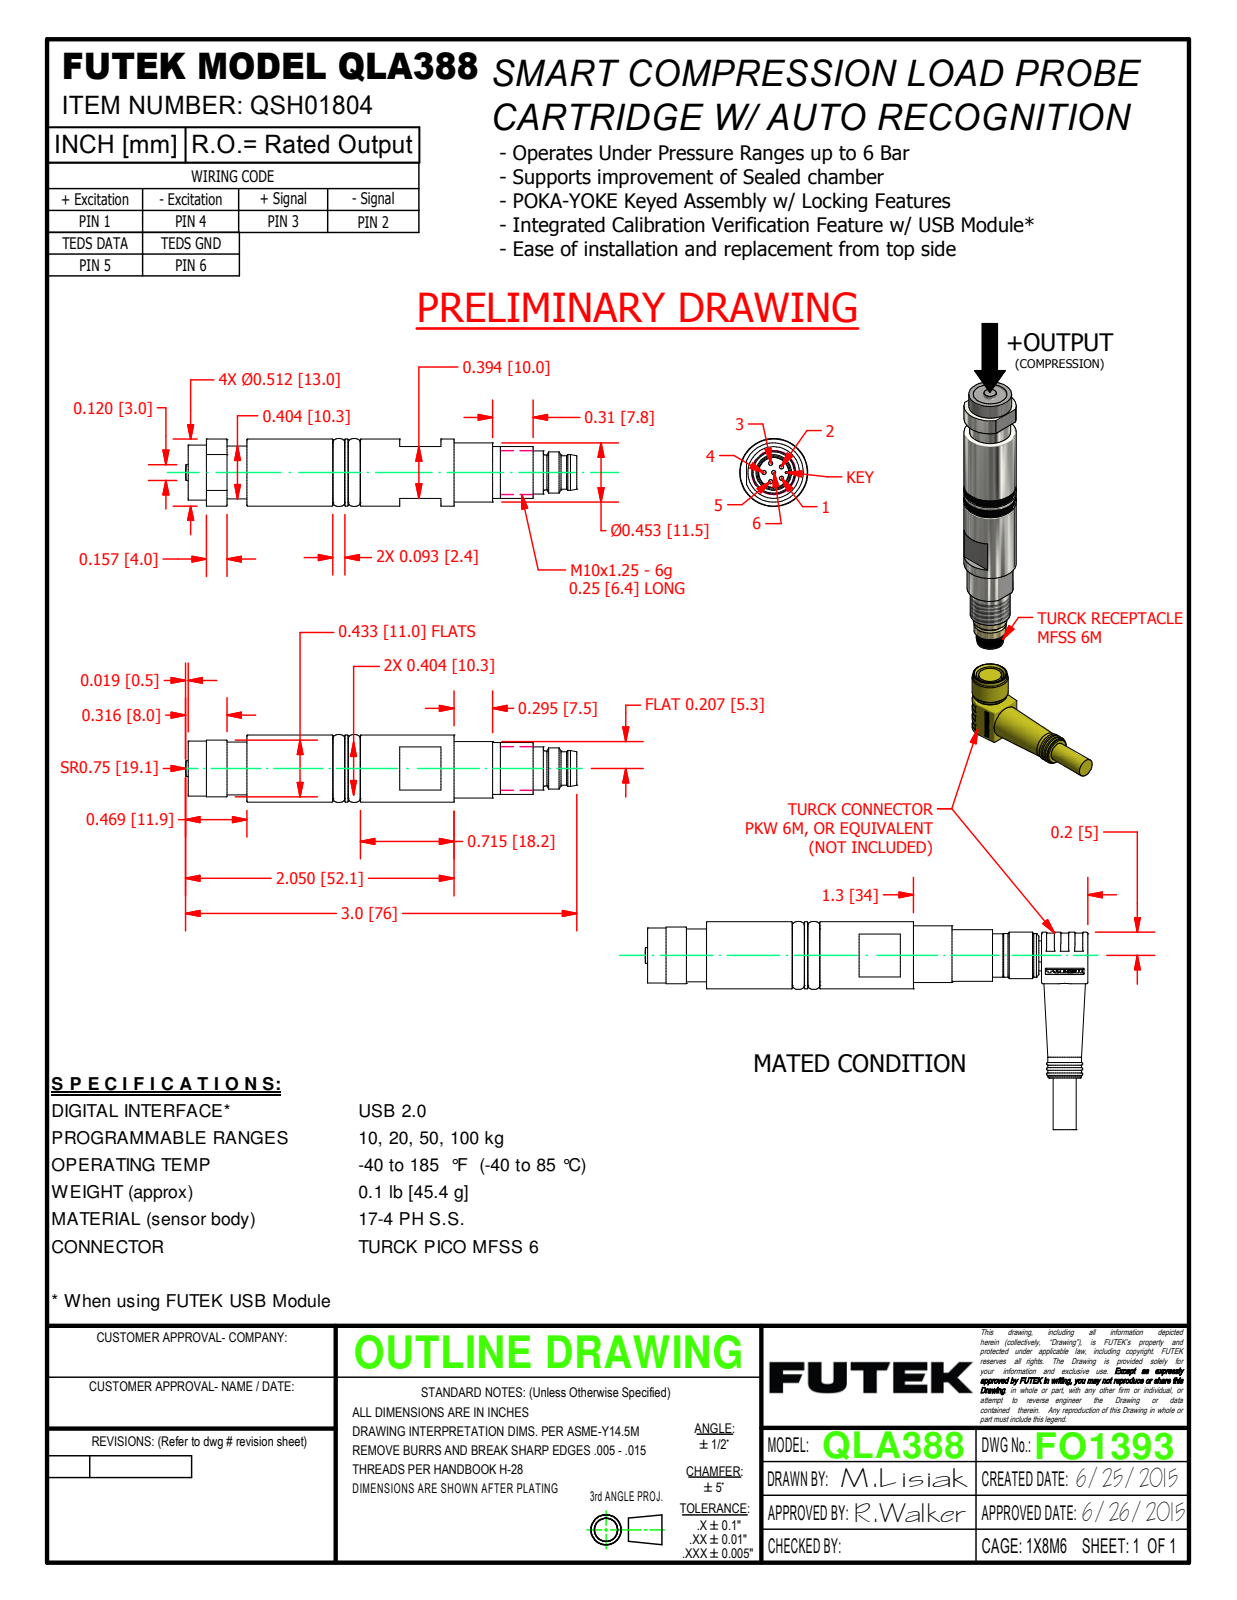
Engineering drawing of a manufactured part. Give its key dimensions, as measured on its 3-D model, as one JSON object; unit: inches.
{"part_name": "QLA388 Assembly_Shrinkwrap_1", "step_written_by": "Autodesk Inventor 2015 (AUTOMOTIVE_DESIGN)", "units": "inches", "bodies": {"solids": 4, "faces": 1420, "planar": 919, "cylindrical": 144, "other": 357}, "overall_size": [3.382, 1.589, 0.52], "round_holes": [[0.177, 1], [0.228, 1], [0.232, 1], [0.26, 1], [0.272, 1], [0.274, 1], [0.283, 1], [0.33, 1]], "round_bosses_or_shafts": [[0.512, 1], [0.453, 1], [0.42, 1], [0.404, 1], [0.394, 1], [0.354, 1], [0.335, 1], [0.331, 1]], "partial_cylinders_radius": [[0.008, 8], [0.012, 8], [0.005, 2], [0.025, 2], [0.108, 1], [0.179, 1], [0.21, 1], [0.256, 1]], "face_to_face_distances": [0.093, 0.118, 0.394, 0.354, 0.719, 0.728, 0.025, 0.866, 2.913, 2.048]}
